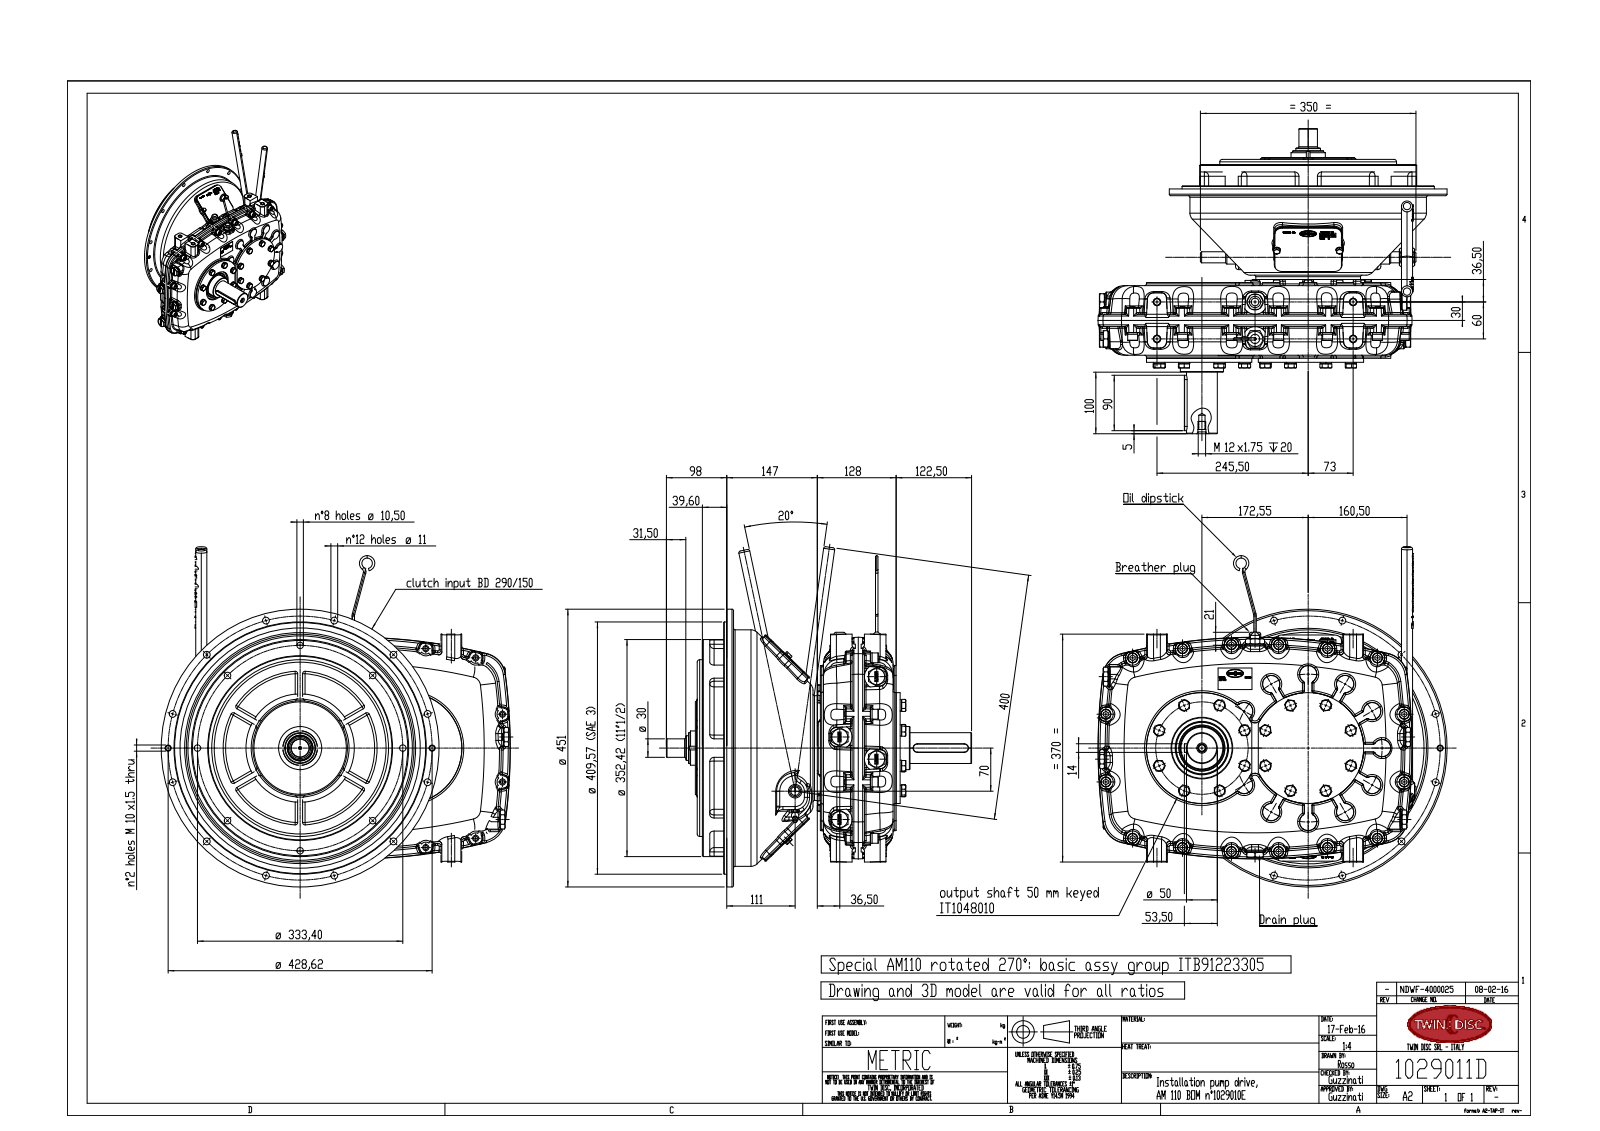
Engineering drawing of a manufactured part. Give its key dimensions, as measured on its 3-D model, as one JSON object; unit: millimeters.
{"part_name": "ITB91210000_rev00-installation; ITam110-013_rev00-installation; IT1048010_rev01-installation; ITam110-010_rev00-installation (+3 more)", "step_written_by": "SolidWorks 2007 (AUTOMOTIVE_DESIGN)", "units": "millimeters", "bodies": {"solids": 25, "faces": 10178, "planar": 3741, "cylindrical": 2065, "other": 4372}, "overall_size": [566.78, 552.47, 495.5], "volume_mm3": 1620000, "surface_area_mm2": 2485000, "round_holes": [[10.2, 48], [11, 44], [8.5, 42], [10.5, 16], [12, 16], [21, 10], [18.63, 9], [5, 6], [6.4, 4], [7, 4], [2.5, 2], [70, 2]], "round_bosses_or_shafts": [[10, 41], [18.1, 16], [16.2, 16], [16.1, 16], [16, 16], [27, 10], [25.95, 10], [20, 7]], "partial_cylinders_radius": [[3, 137], [0.25, 46], [24.86, 46], [12, 40], [15, 32], [4, 30], [7, 30], [10, 20]], "face_to_face_distances": [5, 11, 118, 307, 43, 32, 296, 11.5, 6.5, 123], "hole_center_spacings": [120, 62.12, 102, 231.82, 60, 75, 51.37, 66.61]}
